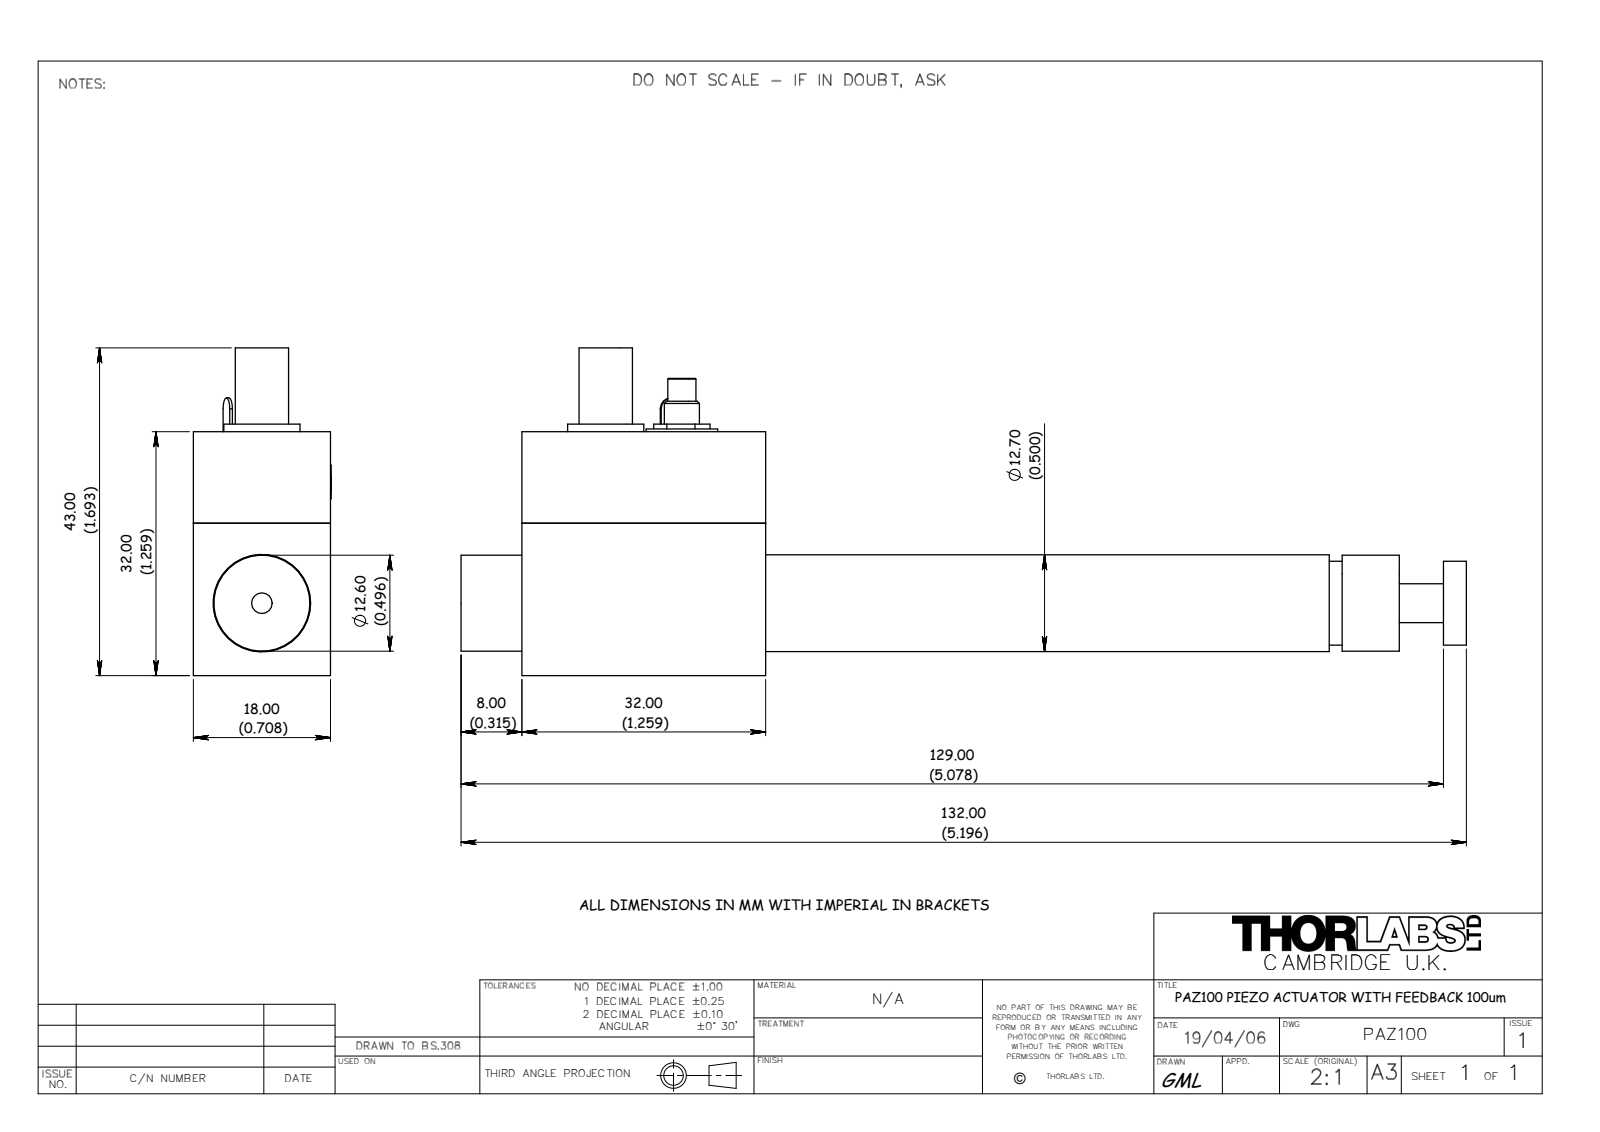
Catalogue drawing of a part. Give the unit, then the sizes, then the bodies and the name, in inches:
Units: inches
Overall size (bounding box): 5.197 × 1.693 × 0.713
Round holes (diameter × count): ⌀0.098 ×2, ⌀0.197 ×2, ⌀0.107 ×1, ⌀0.118 ×1, ⌀0.201 ×1, ⌀0.209 ×1, ⌀0.394 ×1, ⌀0.449 ×1, ⌀0.504 ×1
Round bosses / shafts (diameter × count): ⌀0.5 ×1, ⌀0.496 ×1, ⌀0.433 ×1, ⌀0.37 ×1, ⌀0.354 ×1, ⌀0.276 ×1, ⌀0.201 ×1, ⌀0.181 ×1
Partial cylindrical surfaces — rounded edges, fillets, slot ends (radius × count): R0.059 ×2, R0.087 ×2, R0.057 ×1
Main face-to-face distances: 0.709, 1.26, 0.472, 0.787, 0.315, 1.575, 3.276, 4.535, 4.85, 0.346
Hole centre spacings: 0.315, 0.709, 0.394, 1.024
Bodies: 0 solids, 169 faces (92 planar, 54 cylindrical, 23 other)
Part name (STEP PRODUCT): 15667-E0W
STEP written by: SolidWorks 2007 (AUTOMOTIVE_DESIGN)
